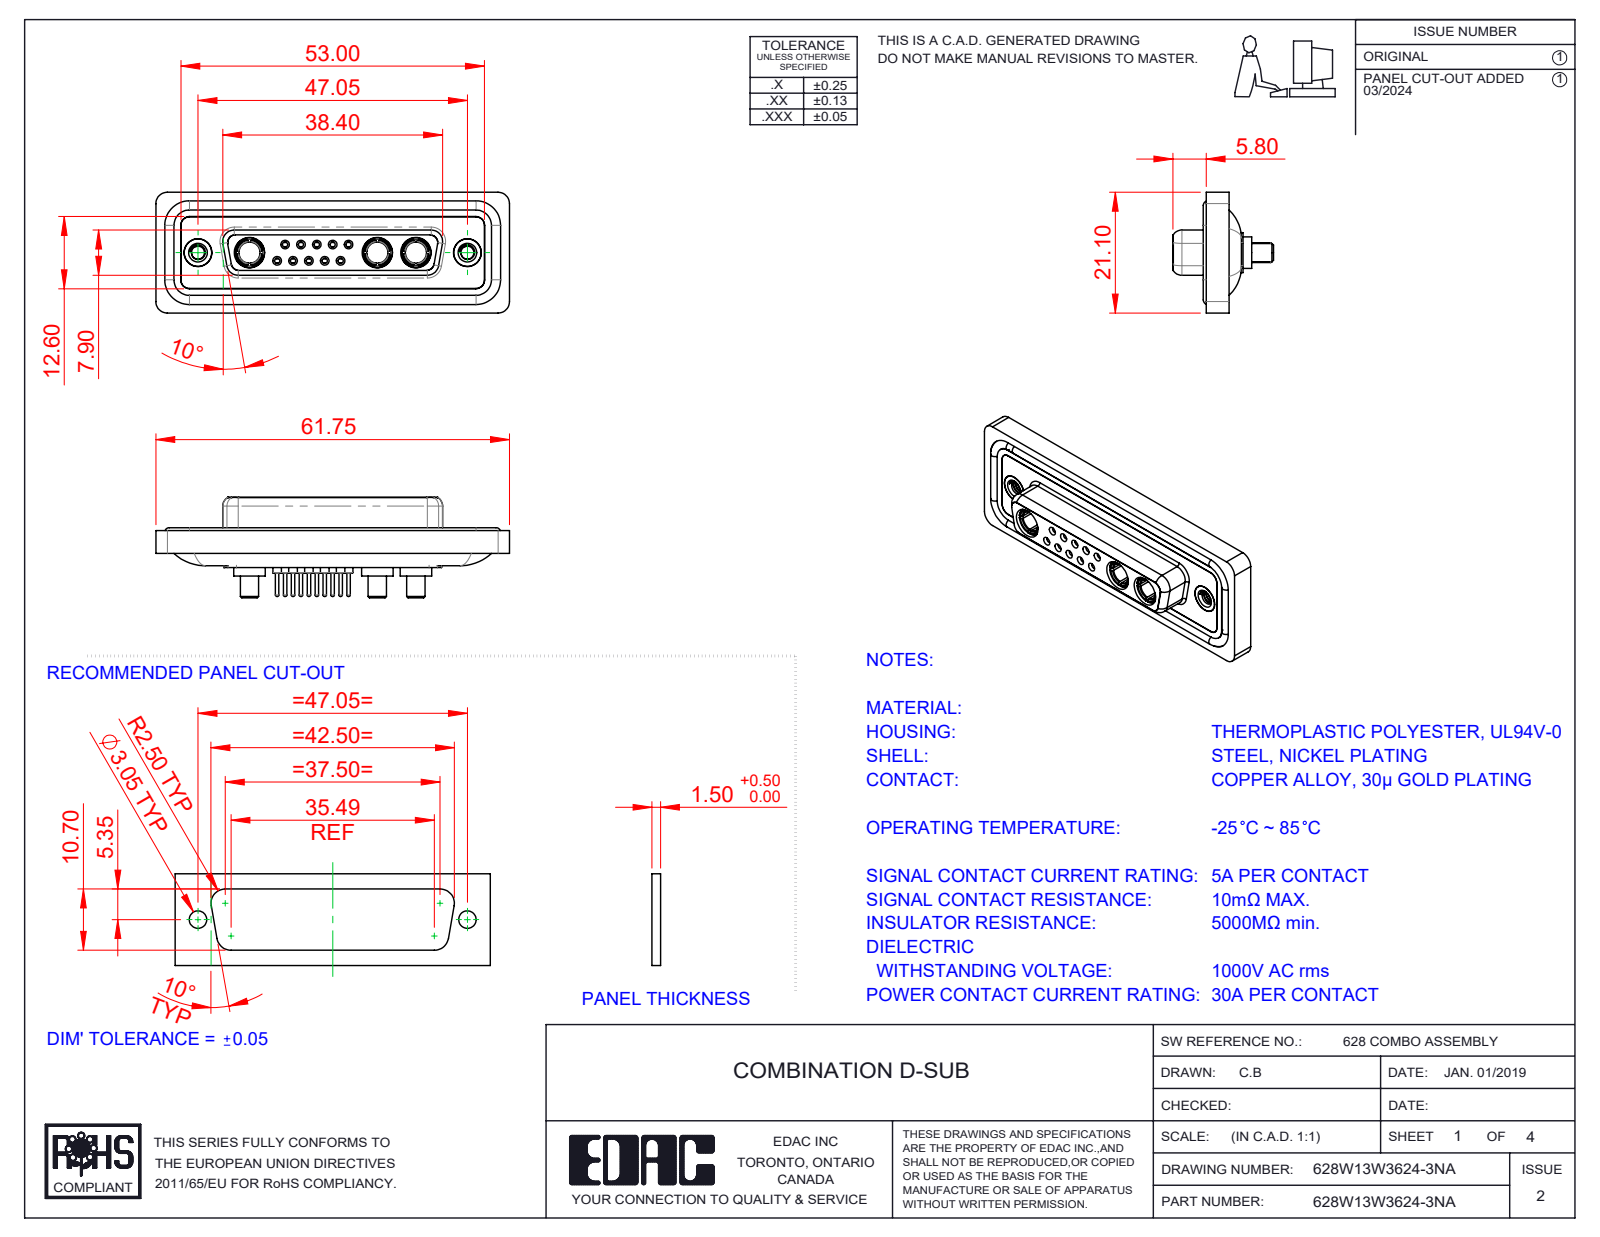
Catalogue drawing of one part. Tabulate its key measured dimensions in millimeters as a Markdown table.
| quantity | value |
| --- | --- |
| part name | 628Combo Threaded Rivet_A; 628Combo Housing_13W3; 628Combo Contact Row 1_24; Power Socket_30A S (+5 more) |
| STEP written by | SolidWorks 2023 (CONFIG_CONTROL_DESIGN) |
| units | millimeters |
| bodies | 23 solids, 1156 faces (342 planar, 449 cylindrical, 365 other) |
| overall size | 61.75 × 21.1 × 17.55 |
| volume | 8 296 mm³ |
| surface area | 13 720 mm² |
| round holes (diameter × count) | 0.9 × 10, 1.1 × 10, 1.5 × 10, 2 × 10, 1.6 × 5, 1.7 × 5, 4.85 × 5, 3.7 × 3, 5.3 × 3, 2.26 × 2, 4 × 2, 4.05 × 2 |
| round bosses / shafts (diameter × count) | 2.2 × 10, 0.6 × 10, 1.6 × 9, 5.5 × 3, 5.2 × 3, 4.96 × 3, 4.75 × 3, 3.75 × 3 |
| partial cylindrical surfaces (radius × count) | 1.5 × 22, 2 × 18, 1.35 × 8, 1.6 × 8, 0.25 × 4, 0.5 × 4, 0.6 × 4, 0.65 × 4 |
| main face-to-face distances | 0.4, 1.8, 7.45, 5.65, 0.5, 6.6, 7.05, 1.6, 2.9, 1.1 |
| hole center spacings | 3.16, 2.77, 5.03, 5.04, 5.54, 8.31, 7.49, 2.76 |
